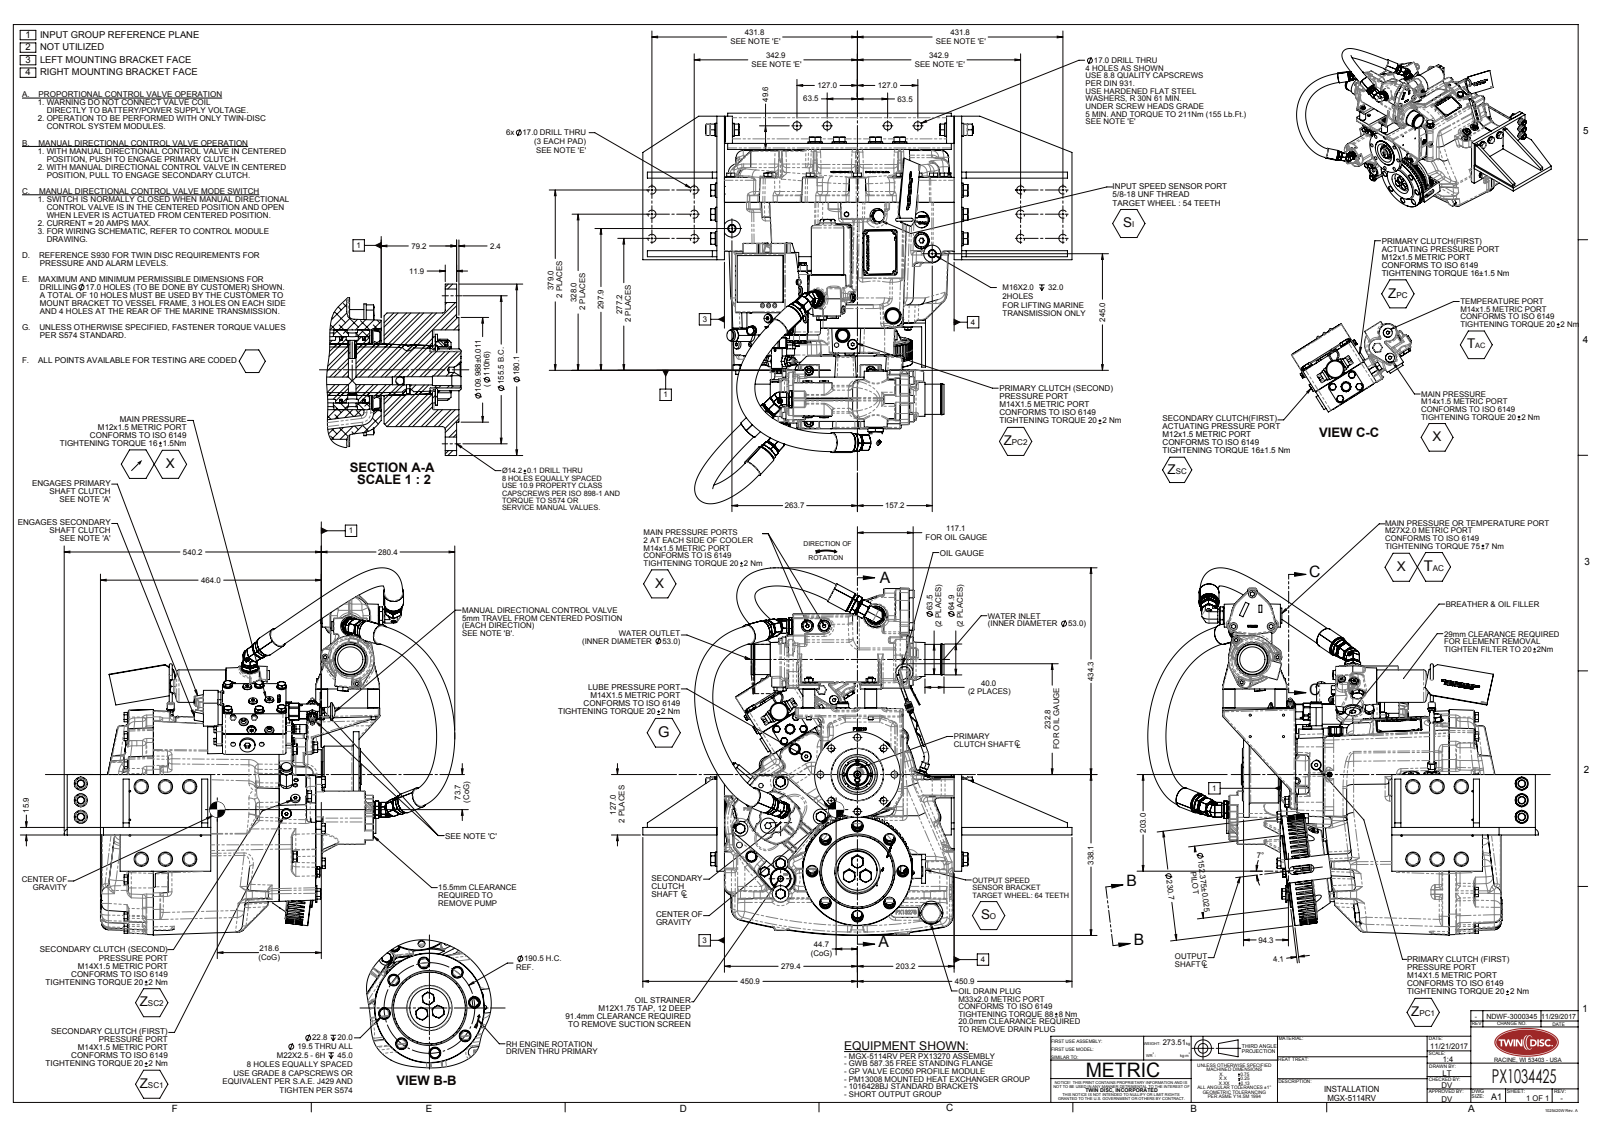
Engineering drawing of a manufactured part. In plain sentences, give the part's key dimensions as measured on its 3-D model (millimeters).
The part is named "PX1034425". Its 3-D file was written by "SolidWorks 2015 (AUTOMOTIVE_DESIGN)". It is 0 solids with 4704 faces: 1630 planar, 1188 cylindrical and 1886 other. Overall it measures 901.7 by 820.68 by 772.4 millimeters. Round holes: 8 of diameter 14.2, 8 of diameter 22.65, 6 of diameter 17, 5 of diameter 10, 5 of diameter 19.5, 5 of diameter 22, 4 of diameter 4.4, 4 of diameter 6.35, 3 of diameter 9.34, 3 of diameter 10.7, 3 of diameter 14, 3 of diameter 16. Round bosses or shafts: 20 of diameter 19.85, 10 of diameter 30, 9 of diameter 18.9, 7 of diameter 24, 7 of diameter 13, 6 of diameter 31.8, 4 of diameter 41.91, 4 of diameter 38.1. Partial cylindrical surfaces (rounded edges, fillets, slot ends): 93 of radius 8, 84 of radius 2, 81 of radius 39.71, 56 of radius 1, 47 of radius 3, 40 of radius 1.5, 40 of radius 4, 35 of radius 7.87. The main face-to-face distances are 15.88, 12.7, 498.48, 0.77, 263.85, 264.62, 111.42, 375.27, 376.04, 111. The hole center spacings are 59.5, 61.54, 72.9, 134.7, 143.65, 176, 82.41, 98.95.
